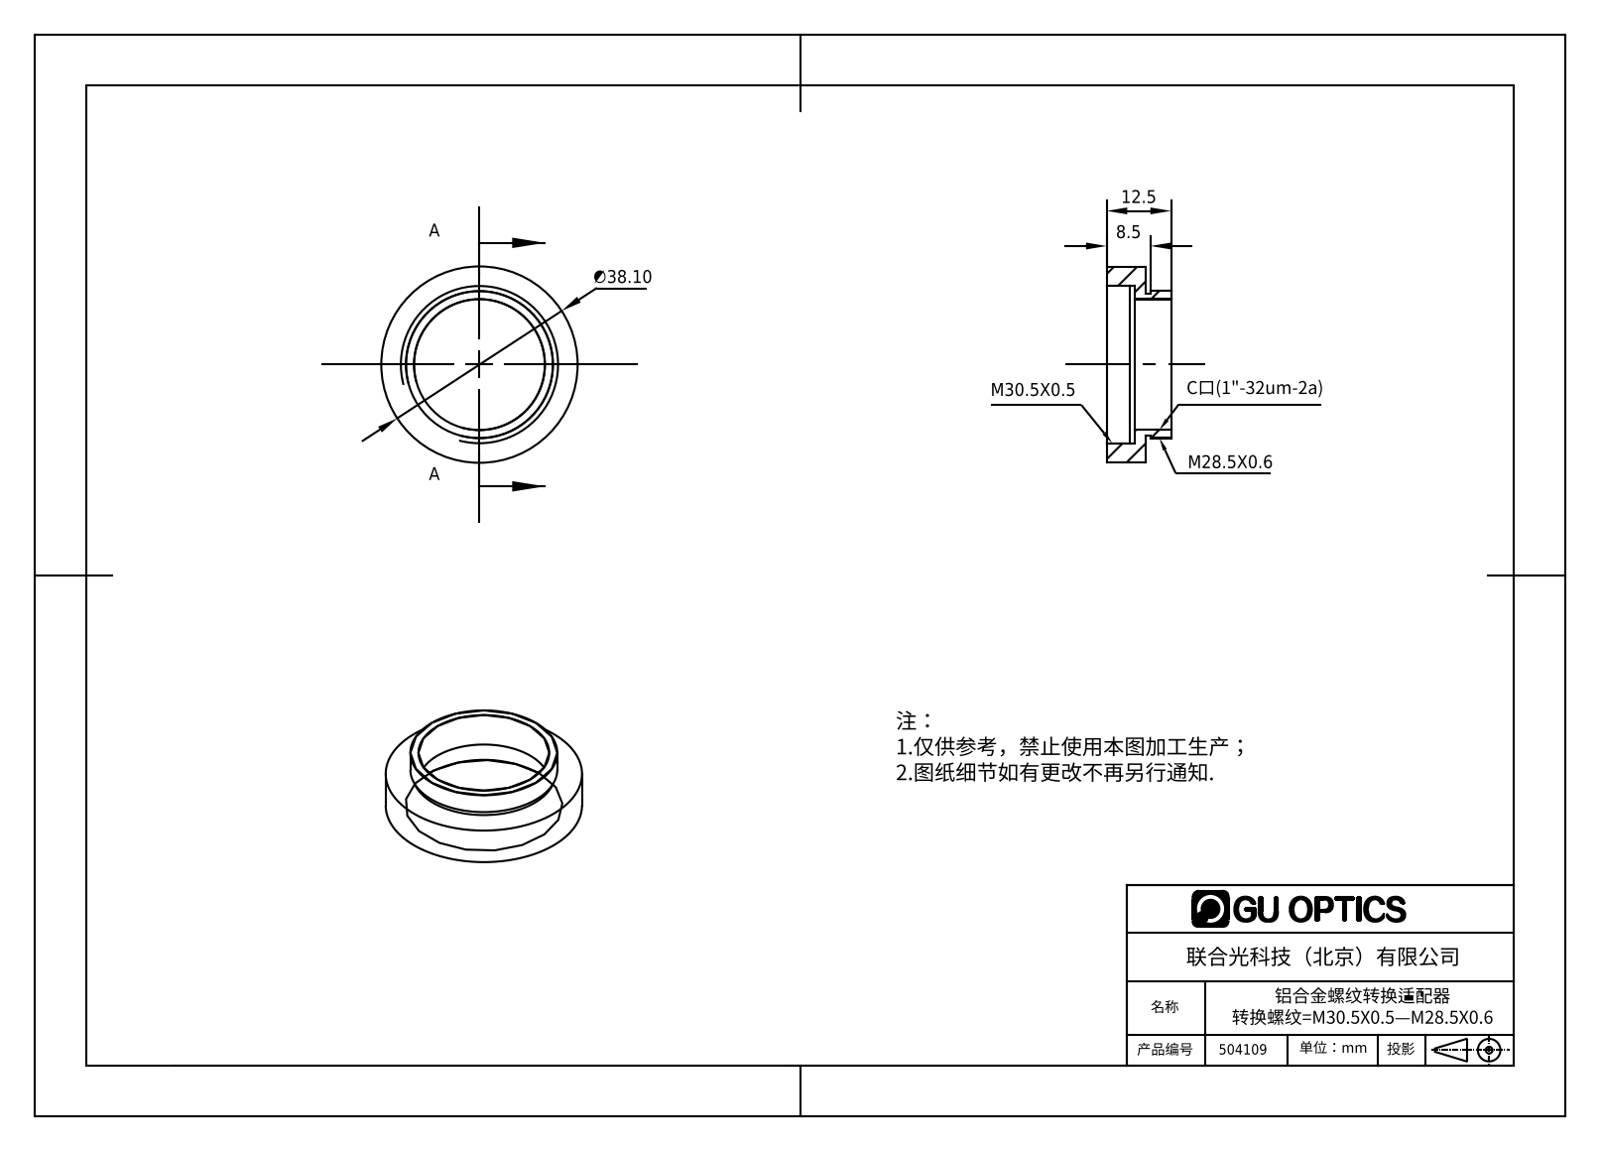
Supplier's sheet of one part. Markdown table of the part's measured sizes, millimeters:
| quantity | value |
| --- | --- |
| part name | 504109 |
| STEP written by | SolidWorks 2016 (AUTOMOTIVE_DESIGN) |
| units | millimeters |
| bodies | 1 solid, 18 faces (6 planar, 12 cylindrical, 0 other) |
| overall size | 38.1 × 38.1 × 12.5 |
| volume | 4 144 mm³ |
| surface area | 3 791 mm² |
| round holes (diameter × count) | 25.38 × 1, 30.48 × 1, 30.7 × 1 |
| round bosses / shafts (diameter × count) | 38.1 × 1, 28.52 × 1, 27.7 × 1 |
| main face-to-face distances | 7.5, 5.5, 2, 12.5, 7, 5, 1, 3, 4, 8.5 |
